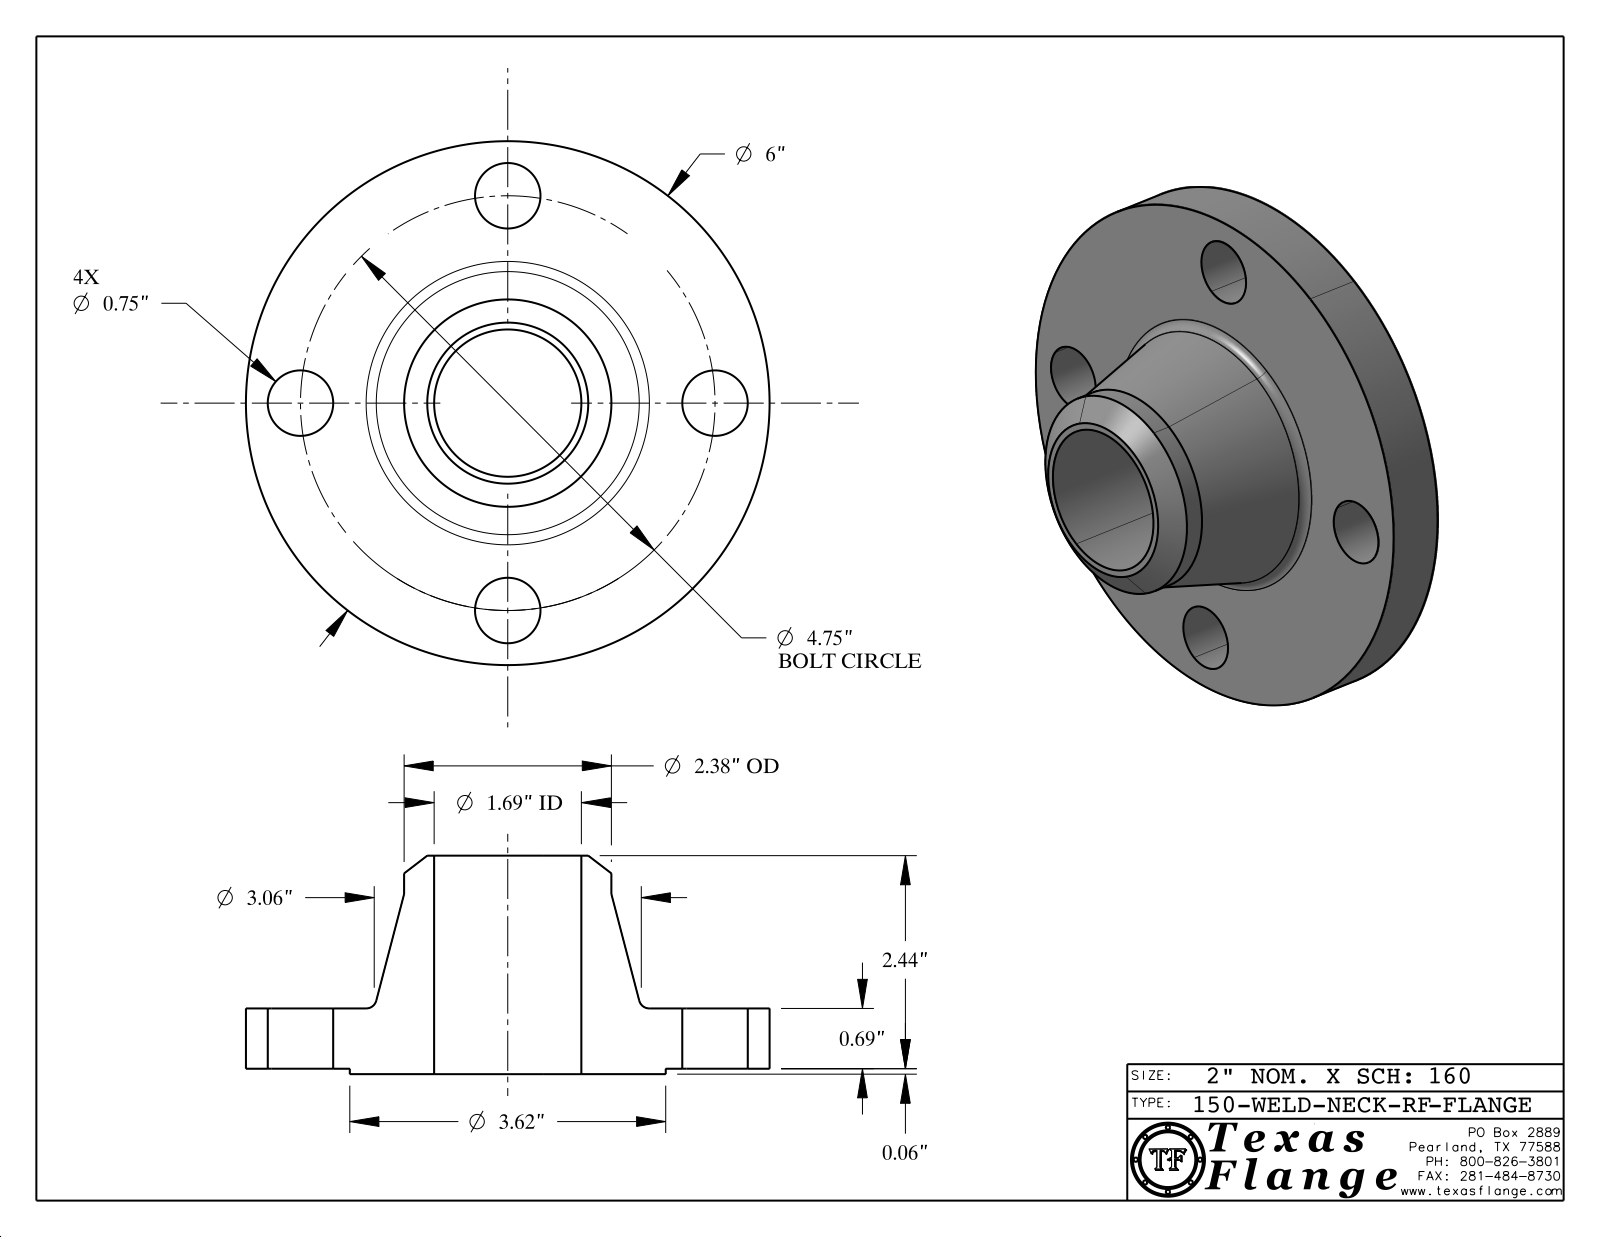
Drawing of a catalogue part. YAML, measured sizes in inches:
part_name: "150-WELD-NECK-RF"
step_written_by: "CATIA V5 STEP AP214 (AUTOMOTIVE_DESIGN)"
units: inches
bodies: {solids: 1, faces: 411, planar: 369, cylindrical: 36, other: 6}
overall_size: [6, 6, 2.503]
volume: 22.76
surface_area: 92.72
round_holes:
  - {diameter: 0.75, count: 4}
  - {diameter: 0.495, count: 1}
  - {diameter: 1.687, count: 1}
round_bosses_or_shafts:
  - {diameter: 0.03, count: 8}
  - {diameter: 6, count: 1}
  - {diameter: 3.62, count: 1}
  - {diameter: 2.375, count: 1}
  - {diameter: 0.39, count: 1}
face_to_face_distances: [0.69, 0.063, 0.753, 2.503, 2.44, 1.75, 0.738, 0.675, 0.015, 1.765]
hole_center_spacings: [2.375, 3.359, 1.818, 4.389, 4.75]
